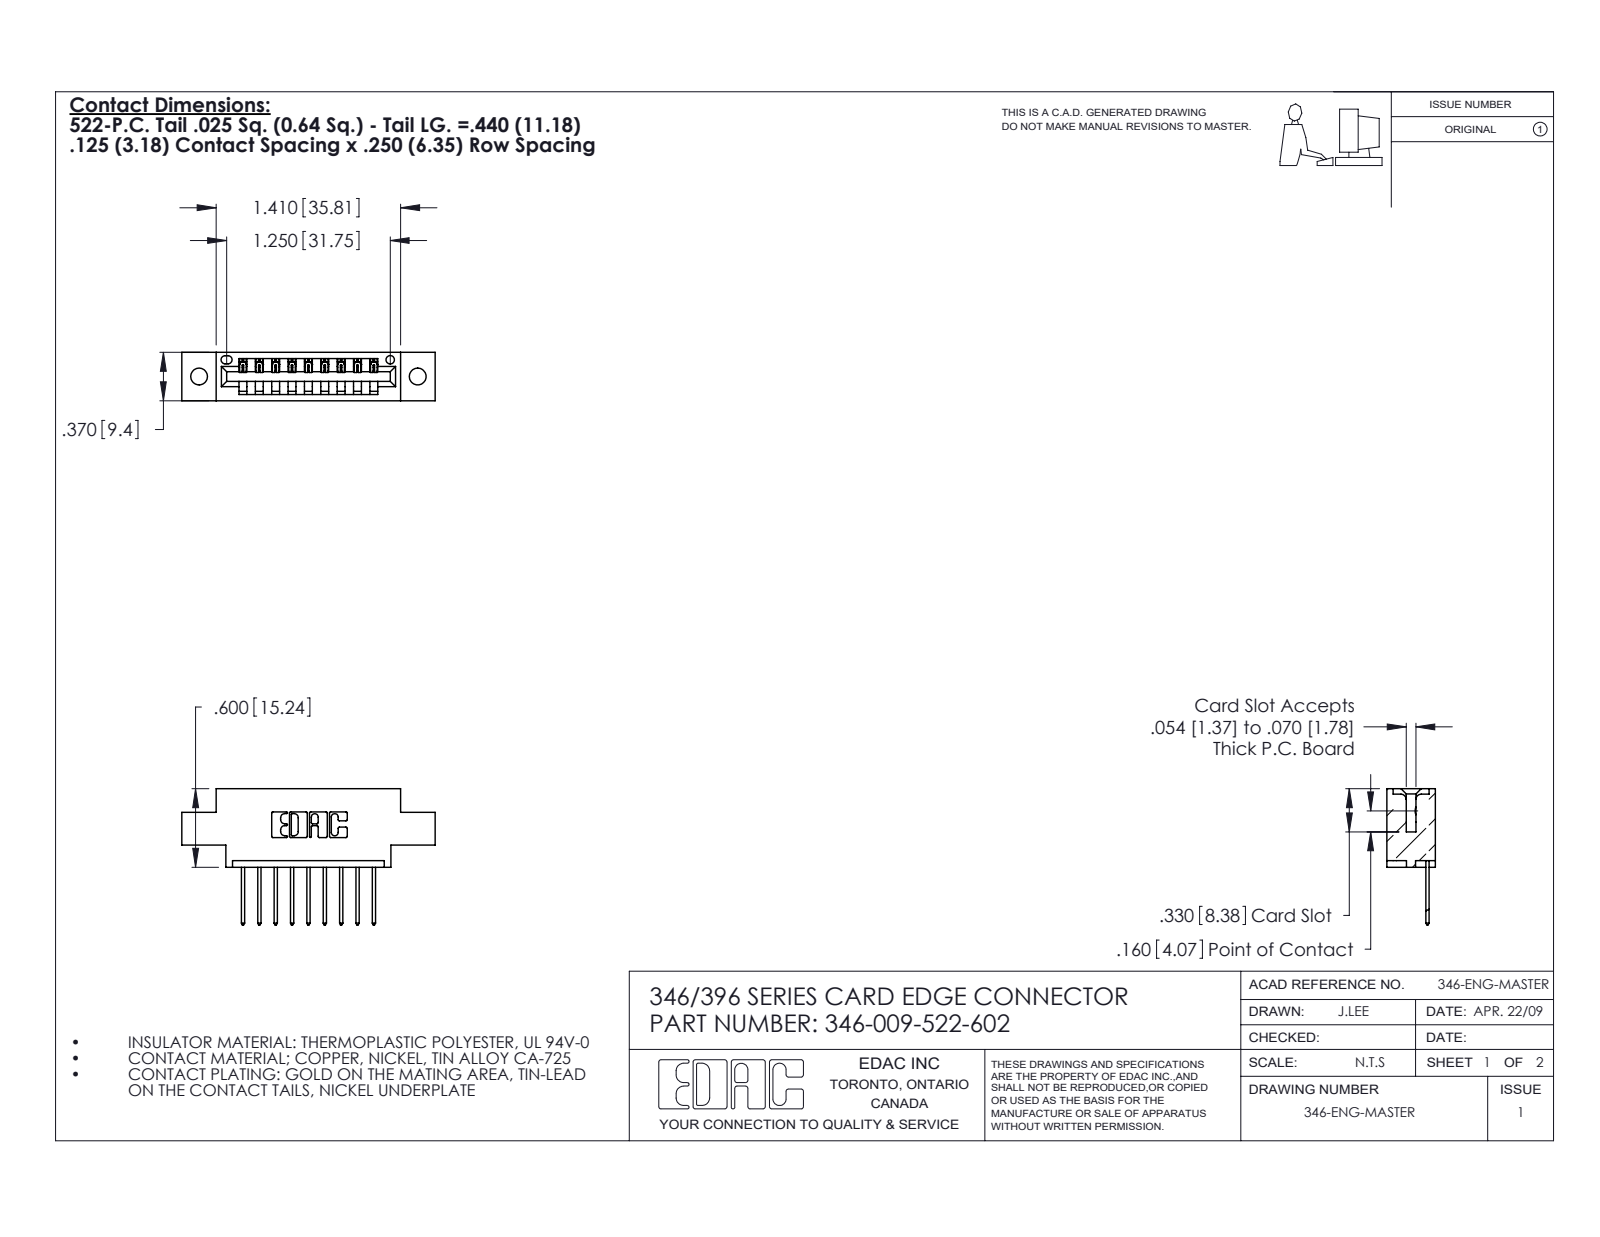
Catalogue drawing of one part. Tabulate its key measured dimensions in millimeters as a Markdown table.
| quantity | value |
| --- | --- |
| part name | 346-009-522-602; 345-292-001_345-293-122; 346 Part_0.170 Offset - 0.128 Dia |
| STEP written by | SolidWorks 2020 (CONFIG_CONTROL_DESIGN) |
| units | millimeters |
| bodies | 10 solids, 648 faces (440 planar, 208 cylindrical, 0 other) |
| overall size | 49.1 × 26.4 × 9.4 |
| volume | 4 290 mm³ |
| surface area | 4 925 mm² |
| round holes (diameter × count) | 3.3 × 2, 1.6 × 1 |
| partial cylindrical surfaces (radius × count) | 0.3 × 22, 0.2 × 18, 0.3 × 18, 0.2 × 6, 0.8 × 6, 0.7 × 3, 0.8 × 2, 1 × 2 |
| main face-to-face distances | 6.4, 9.4, 1.2, 8.2, 1.8, 7.6, 0.6, 3.8, 5.6, 2.5 |
| hole center spacings | 6.2, 37.2, 42.4 |
